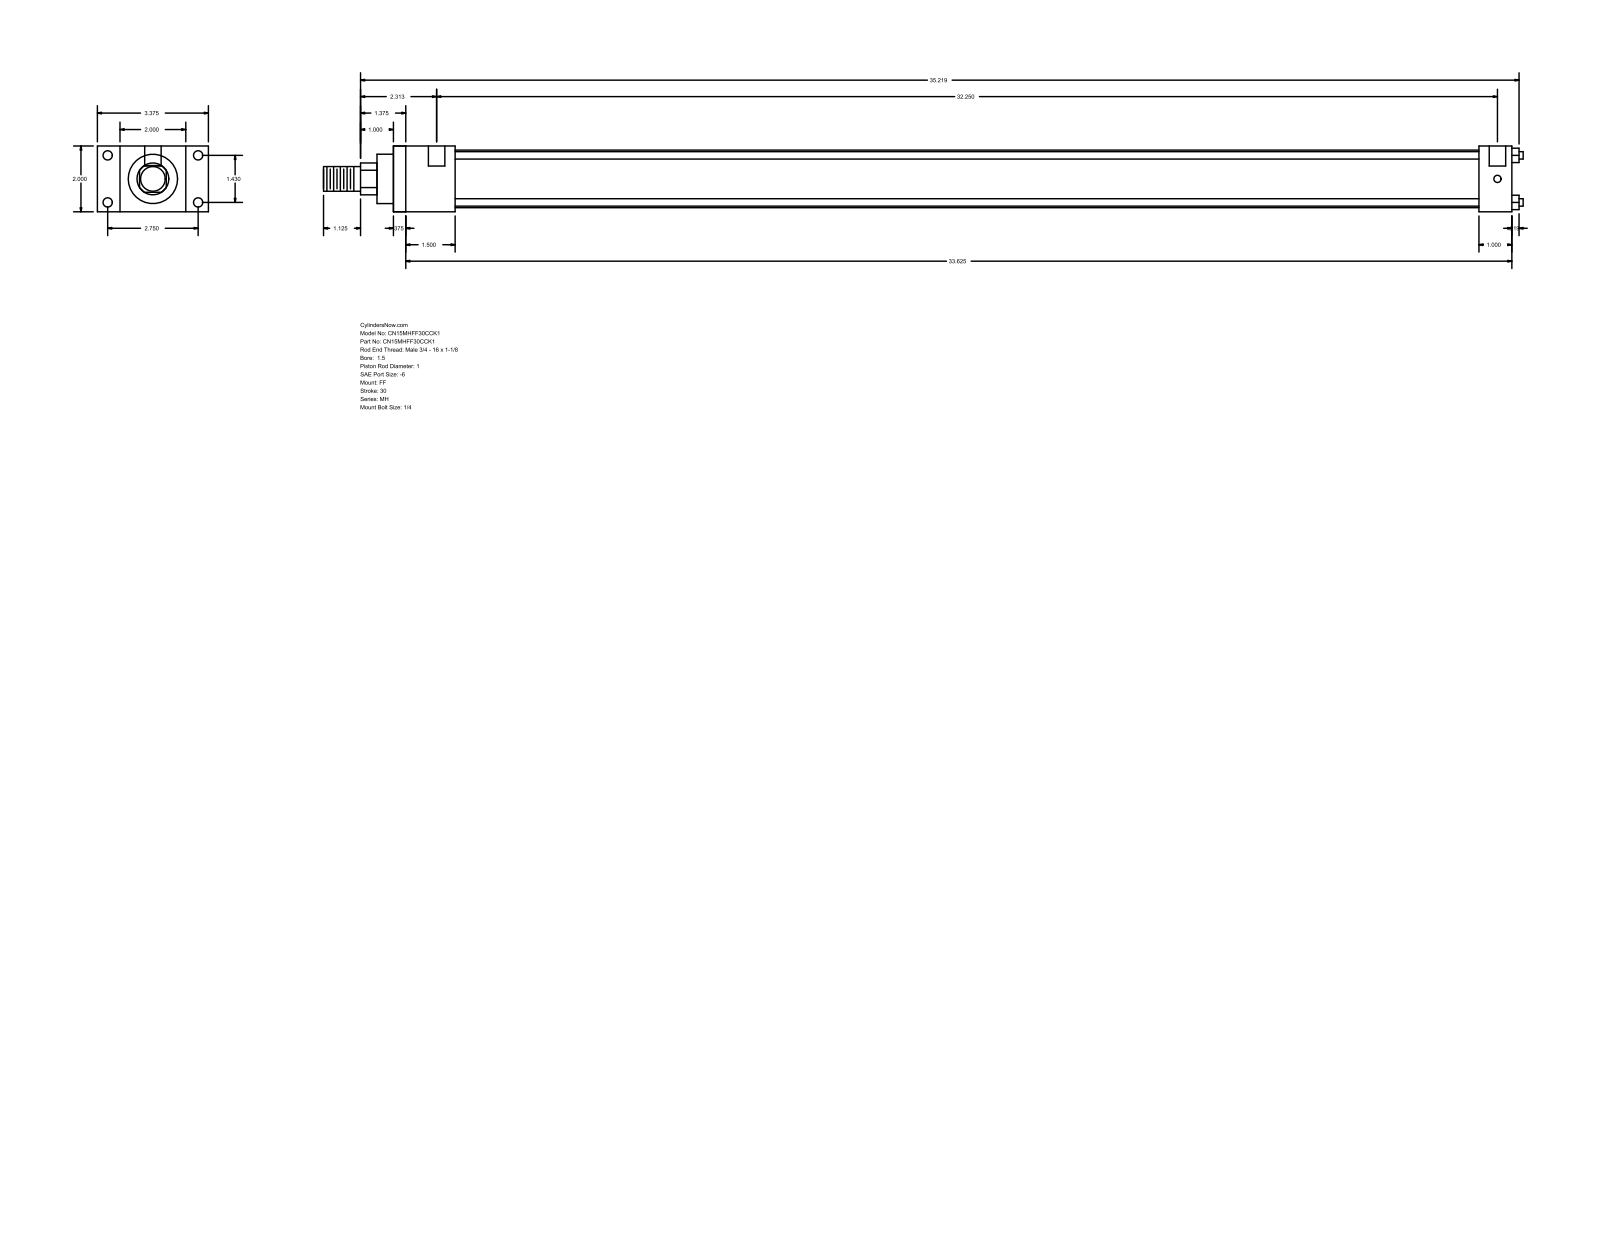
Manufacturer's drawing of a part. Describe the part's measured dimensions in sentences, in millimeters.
The part is named "MH_FF__0150_1". Its 3-D file was written by "GSSL Pune (CONFIG_CONTROL_DESIGN)". It is 0 solids with 92 faces: 64 planar, 28 cylindrical and 0 other. Overall it measures 926.31 by 85.72 by 50.8 millimeters. Round holes: 4 of diameter 5.56, 4 of diameter 7.14, 2 of diameter 12.7. Round bosses or shafts: 4 of diameter 5.71, 1 of diameter 44.45, 1 of diameter 38.1, 1 of diameter 25.4, 1 of diameter 19.05. Partial cylindrical surfaces (rounded edges, fillets, slot ends): 1 of radius 12.29. The main face-to-face distances are 50.8, 863.6, 9.52, 854.08, 25.4, 17.46, 68.26, 47.63, 38.11, 815.97. The hole center spacings are 36.32, 69.84, 78.72, 822.33, 3.18, 819.15.
